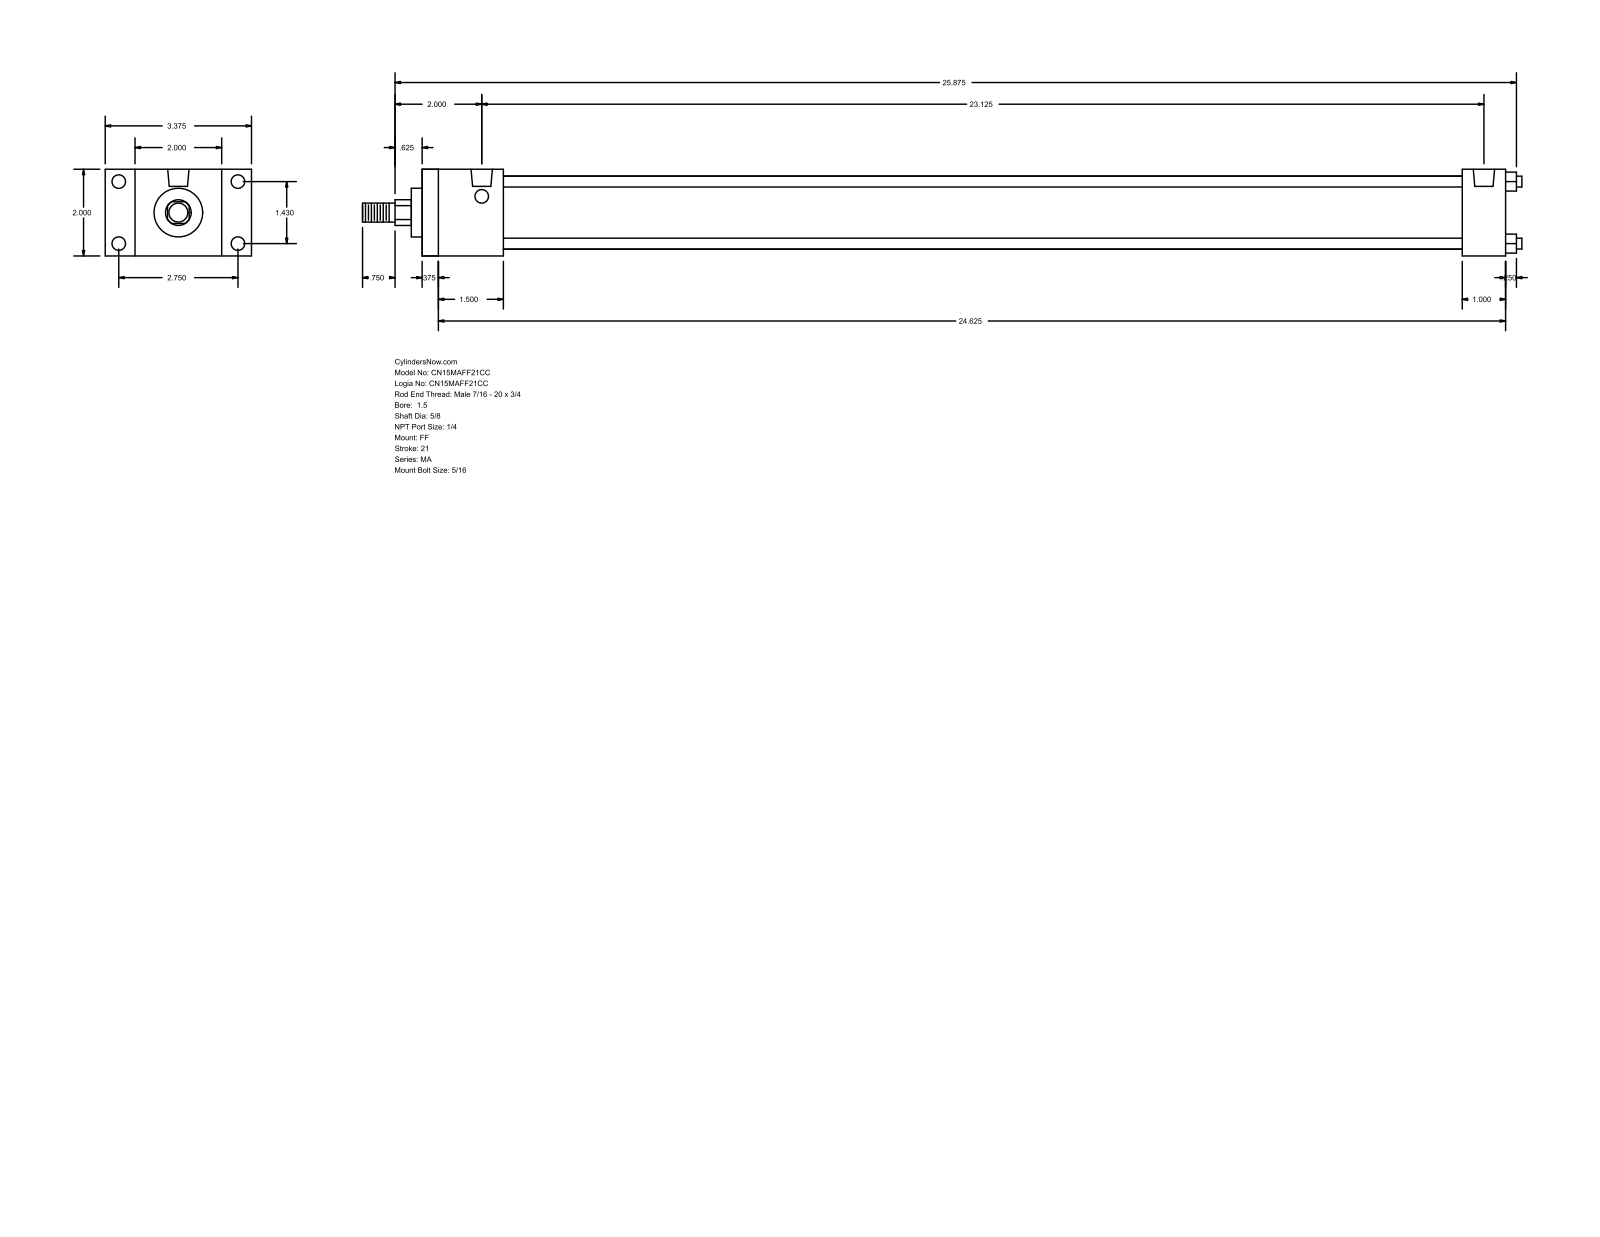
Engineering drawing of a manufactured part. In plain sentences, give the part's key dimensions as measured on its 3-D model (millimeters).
The part is named "MA_FF__0150_0.625". Its 3-D file was written by "GSSL Pune (CONFIG_CONTROL_DESIGN)". It is 0 solids with 92 faces: 64 planar, 28 cylindrical and 0 other. Overall it measures 679.45 by 85.72 by 50.8 millimeters. Round holes: 8 of diameter 7.94, 2 of diameter 12.49. Round bosses or shafts: 4 of diameter 6.35, 1 of diameter 42.93, 1 of diameter 28.57, 1 of diameter 15.88, 1 of diameter 11.11. Partial cylindrical surfaces (rounded edges, fillets, slot ends): 1 of radius 7.54. The main face-to-face distances are 50.8, 635, 9.52, 625.48, 25.4, 47.62, 609.6, 38.1, 600.08, 561.98. The hole center spacings are 36.32, 69.84, 78.72, 587.37.
